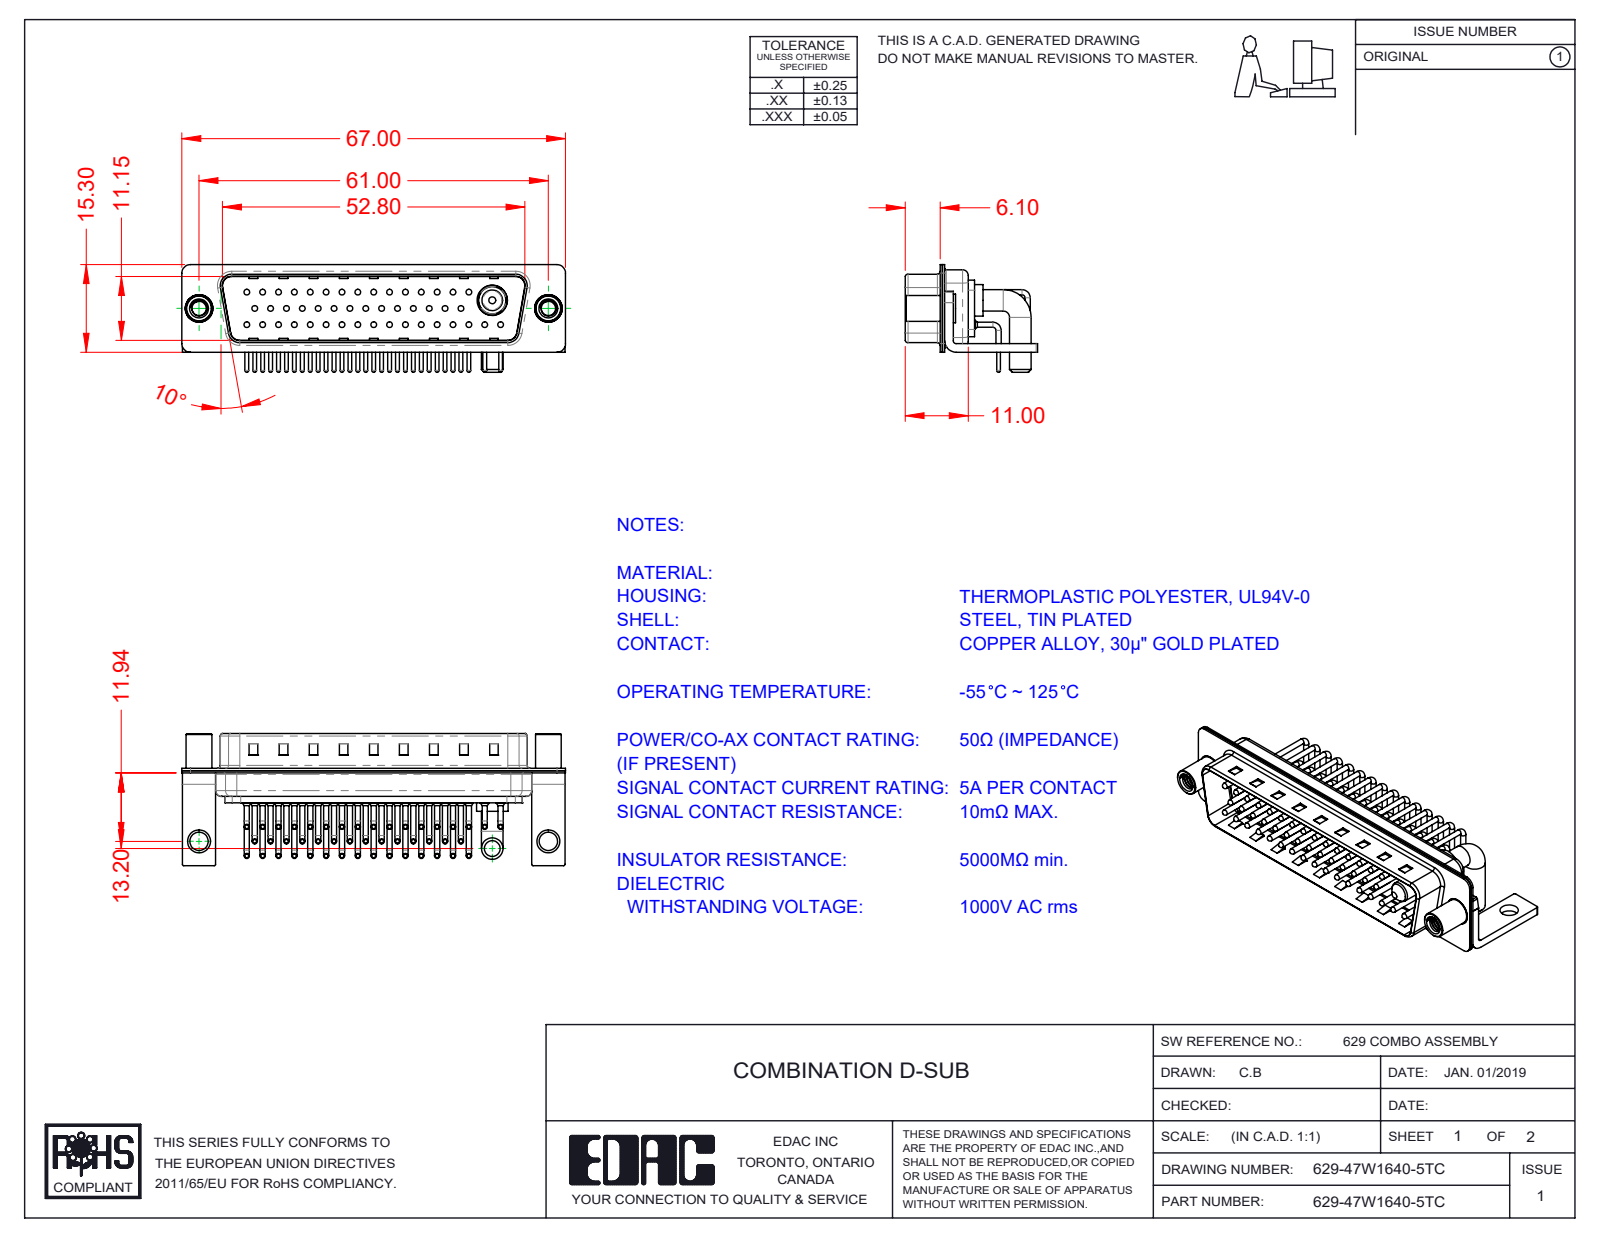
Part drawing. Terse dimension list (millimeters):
name: 629Combo Stabilizer Bracket_50 Contacts; 629-47W1640-5TC; 629Combo Contact Row 3; 629Combo Contact Row 1_50 Contacts (+6 more)
written by: SolidWorks 2020 (CONFIG_CONTROL_DESIGN)
unit: mm
bodies: 55 solids, 5613 faces (3179 planar, 1890 cylindrical, 544 other)
size: 67 × 23.1 × 18.8
volume: 5 656 mm³; area: 13 849 mm²
holes: 46× ⌀0.75, 46× ⌀1.6, 46× ⌀2, 2× ⌀2.5, 2× ⌀3.2, 2× ⌀4, 2× ⌀4.8, 1× ⌀4.85, 1× ⌀5.3
bosses: 92× ⌀0.9, 46× ⌀1.5, 46× ⌀1, 46× ⌀0.65, 2× ⌀5, 2× ⌀4.9, 2× ⌀4.5, 2× ⌀3.75
rounds: 46× R1.01, 16× R0.25, 16× R1.5, 13× R2, 9× R0.5, 8× R1.6, 4× R0.6, 4× R0.65
face distances: 0.4, 1.5, 11.55, 5.6, 4.1, 1.9, 5.2, 0.8, 6, 1.1
hole spacings: 2.77, 3.16, 5.54, 8.31, 11.08, 13.85, 16.62, 19.39
